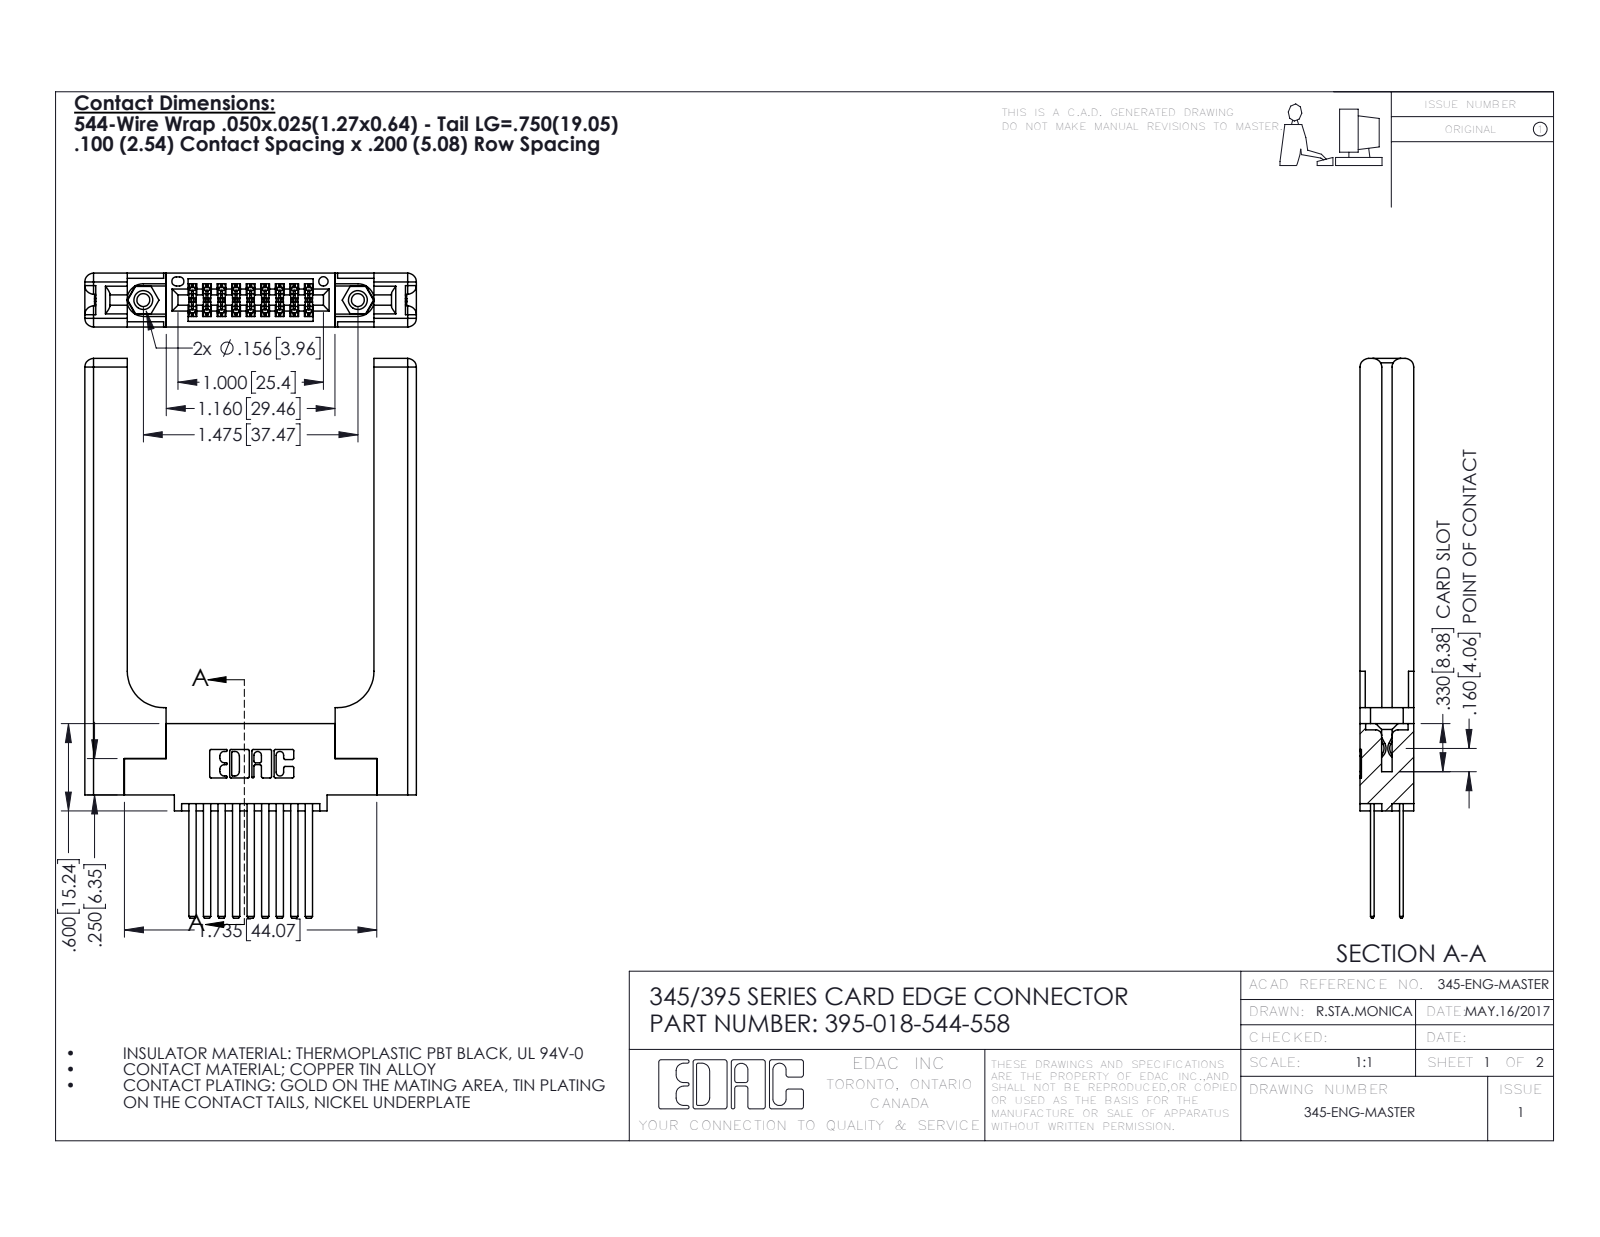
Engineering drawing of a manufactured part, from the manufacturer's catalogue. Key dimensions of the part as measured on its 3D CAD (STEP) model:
Part name (STEP PRODUCT): 345-292-001_345-293-144; 345 Part_0.110 Offset - 0.156 Dia-TH; 395-018-544-558; 345-250-001_345-250-001-102 (+1 more)
STEP written by: SolidWorks 2016 (CONFIG_CONTROL_DESIGN)
Units: inches
Bodies: 23 solids, 1178 faces (754 planar, 364 cylindrical, 60 other)
Overall size (bounding box): 3.847 × 2.279 × 0.37
Volume: 0.853 in³ · Surface area: 20.73 in²
Round holes (diameter × count): ⌀0.089 ×2, ⌀0.125 ×2, ⌀0.156 ×2, ⌀0.064 ×1
Round bosses / shafts (diameter × count): ⌀0.155 ×2
Partial cylindrical surfaces — rounded edges, fillets, slot ends (radius × count): R0.006 ×27, R0.01 ×22, R0.06 ×16, R0.007 ×6, R0.031 ×6, R0.026 ×3, R0.014 ×2, R0.019 ×2
Main face-to-face distances: 0.37, 0.072, 0.298, 0.15, 0.077, 0.148, 0.098, 0.272, 0.025, 0.2
Hole centre spacings: 0.27, 1.244, 1.475
